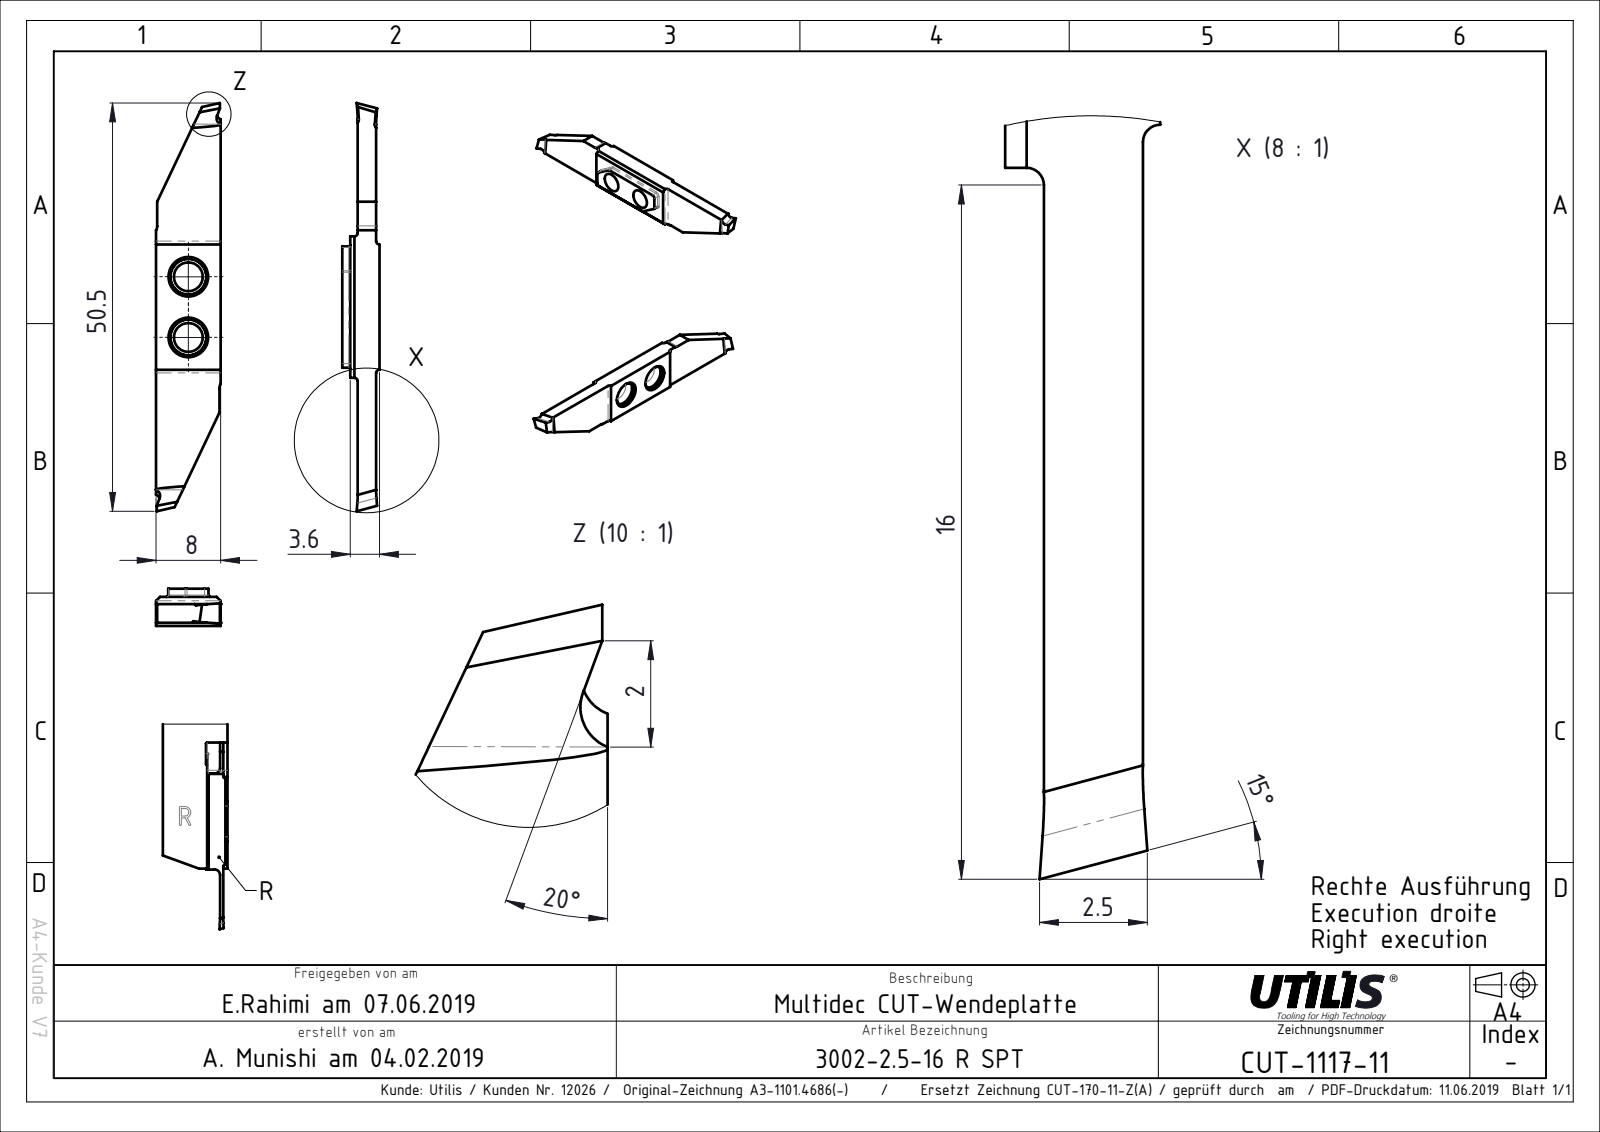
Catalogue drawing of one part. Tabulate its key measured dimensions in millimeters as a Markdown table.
| quantity | value |
| --- | --- |
| part name | CUT-1117; ASME Y14.5 |
| STEP written by | FormatWorks Professional (AP242_MANAGED_MODEL_BASED_3D_ENGINEERING_MIM_LF) |
| units | millimeters |
| bodies | 1 solid, 34 faces (24 planar, 10 cylindrical, 0 other) |
| overall size | 50.5 × 8 × 3.6 |
| volume | 852 mm³ |
| surface area | 991 mm² |
| round holes (diameter × count) | 3.55 × 2 |
| partial cylindrical surfaces (radius × count) | 0.4 × 4, 1 × 2 |
| main face-to-face distances | 2.28, 2.69, 0.41, 0.91, 3.19, 3.6, 8, 18.09, 7.85, 7.7 |
| hole center spacings | 7.5 |
